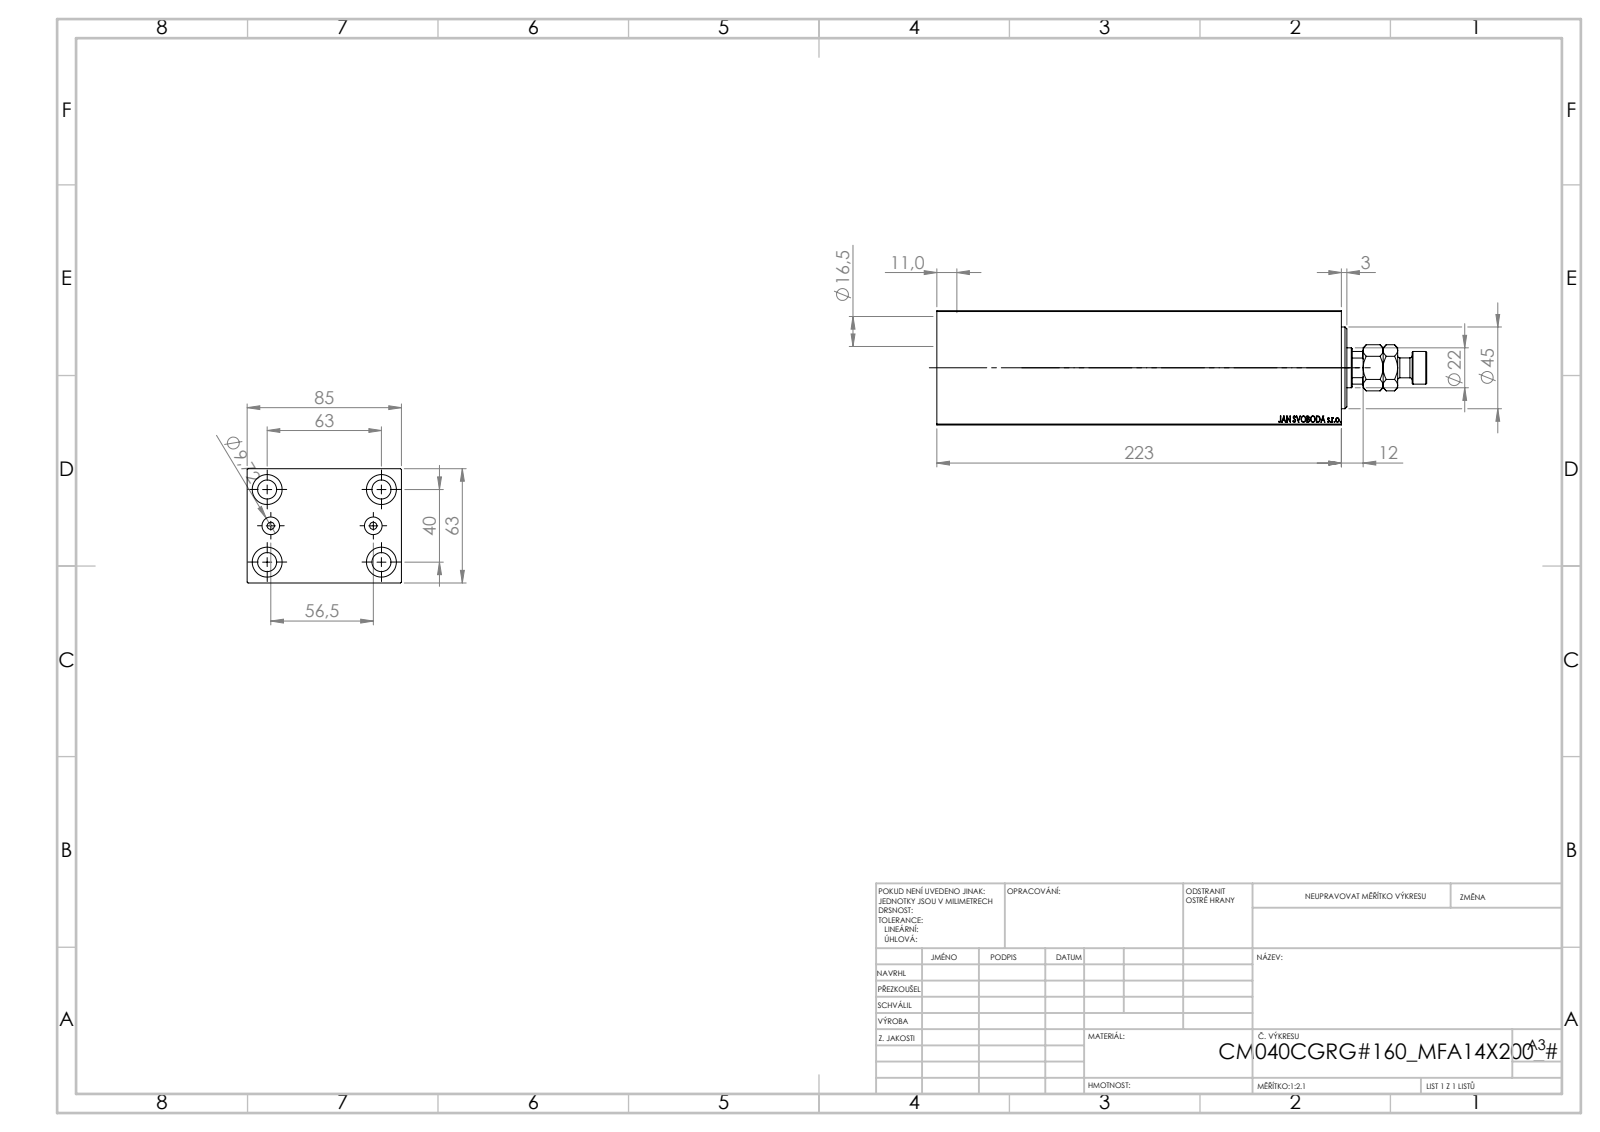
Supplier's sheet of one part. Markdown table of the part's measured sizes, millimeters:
| quantity | value |
| --- | --- |
| part name | V450CM_VC_B; MFA; V450CM_C_Body; V450CM_C_VCP |
| STEP written by | SolidWorks 2019 (CONFIG_CONTROL_DESIGN) |
| units | millimeters |
| bodies | 4 solids, 910 faces (424 planar, 60 cylindrical, 426 other) |
| overall size | 269 × 85 × 63 |
| volume | 1 105 000 mm³ |
| surface area | 138 549 mm² |
| round holes (diameter × count) | 10.5 × 4, 16.5 × 4, 4 × 2, 9.72 × 2, 12.5 × 1, 22 × 1, 25.5 × 1, 40 × 1, 42 × 1, 45 × 1 |
| round bosses / shafts (diameter × count) | 18 × 1, 11 × 1 |
| partial cylindrical surfaces (radius × count) | 10.5 × 1 |
| main face-to-face distances | 63, 85, 223, 51, 172, 11, 8, 22, 21.6, 29.4 |
| hole center spacings | 20.26, 37.31, 63.01, 28.25, 40, 63, 74.63, 56.5 |
